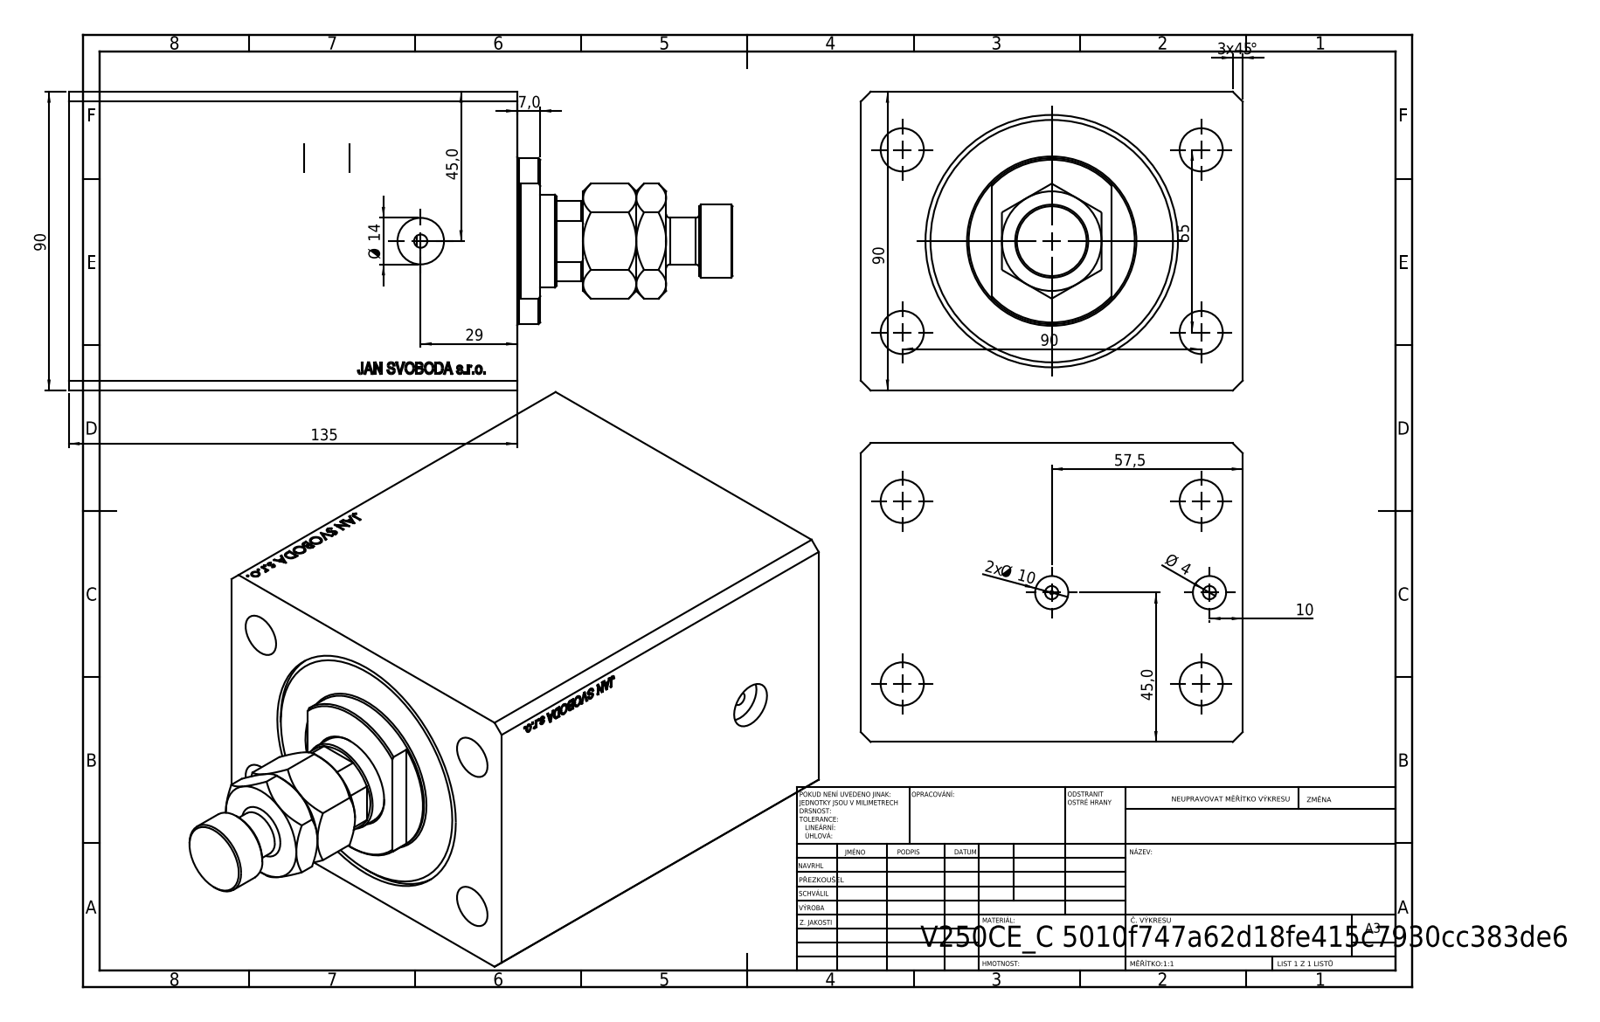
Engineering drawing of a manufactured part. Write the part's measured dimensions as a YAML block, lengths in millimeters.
part_name: "V250CE_VC_C; V250CE_C_Body; MFA; V250CE_C_VCP"
step_written_by: "SolidWorks 2019 (CONFIG_CONTROL_DESIGN)"
units: millimeters
bodies: {solids: 4, faces: 920, planar: 444, cylindrical: 50, other: 426}
overall_size: [199.9, 115, 90]
volume: 1228000
surface_area: 172105
round_holes:
  - {diameter: 4, count: 4}
  - {diameter: 13, count: 4}
  - {diameter: 10, count: 2}
  - {diameter: 14, count: 2}
  - {diameter: 1.25, count: 1}
  - {diameter: 18.5, count: 1}
  - {diameter: 28, count: 1}
  - {diameter: 63, count: 1}
  - {diameter: 76, count: 1}
round_bosses_or_shafts:
  - {diameter: 50, count: 1}
  - {diameter: 22, count: 1}
  - {diameter: 14, count: 1}
partial_cylinders:
  - {radius: 13.5, count: 1}
face_to_face_distances: [90, 115, 135, 17.9, 117.1, 104.9, 87, 30.1, 50, 54.9]
hole_center_spacings: [52.74, 27.61, 55, 90, 96.5, 105.48, 47.5, 77]
